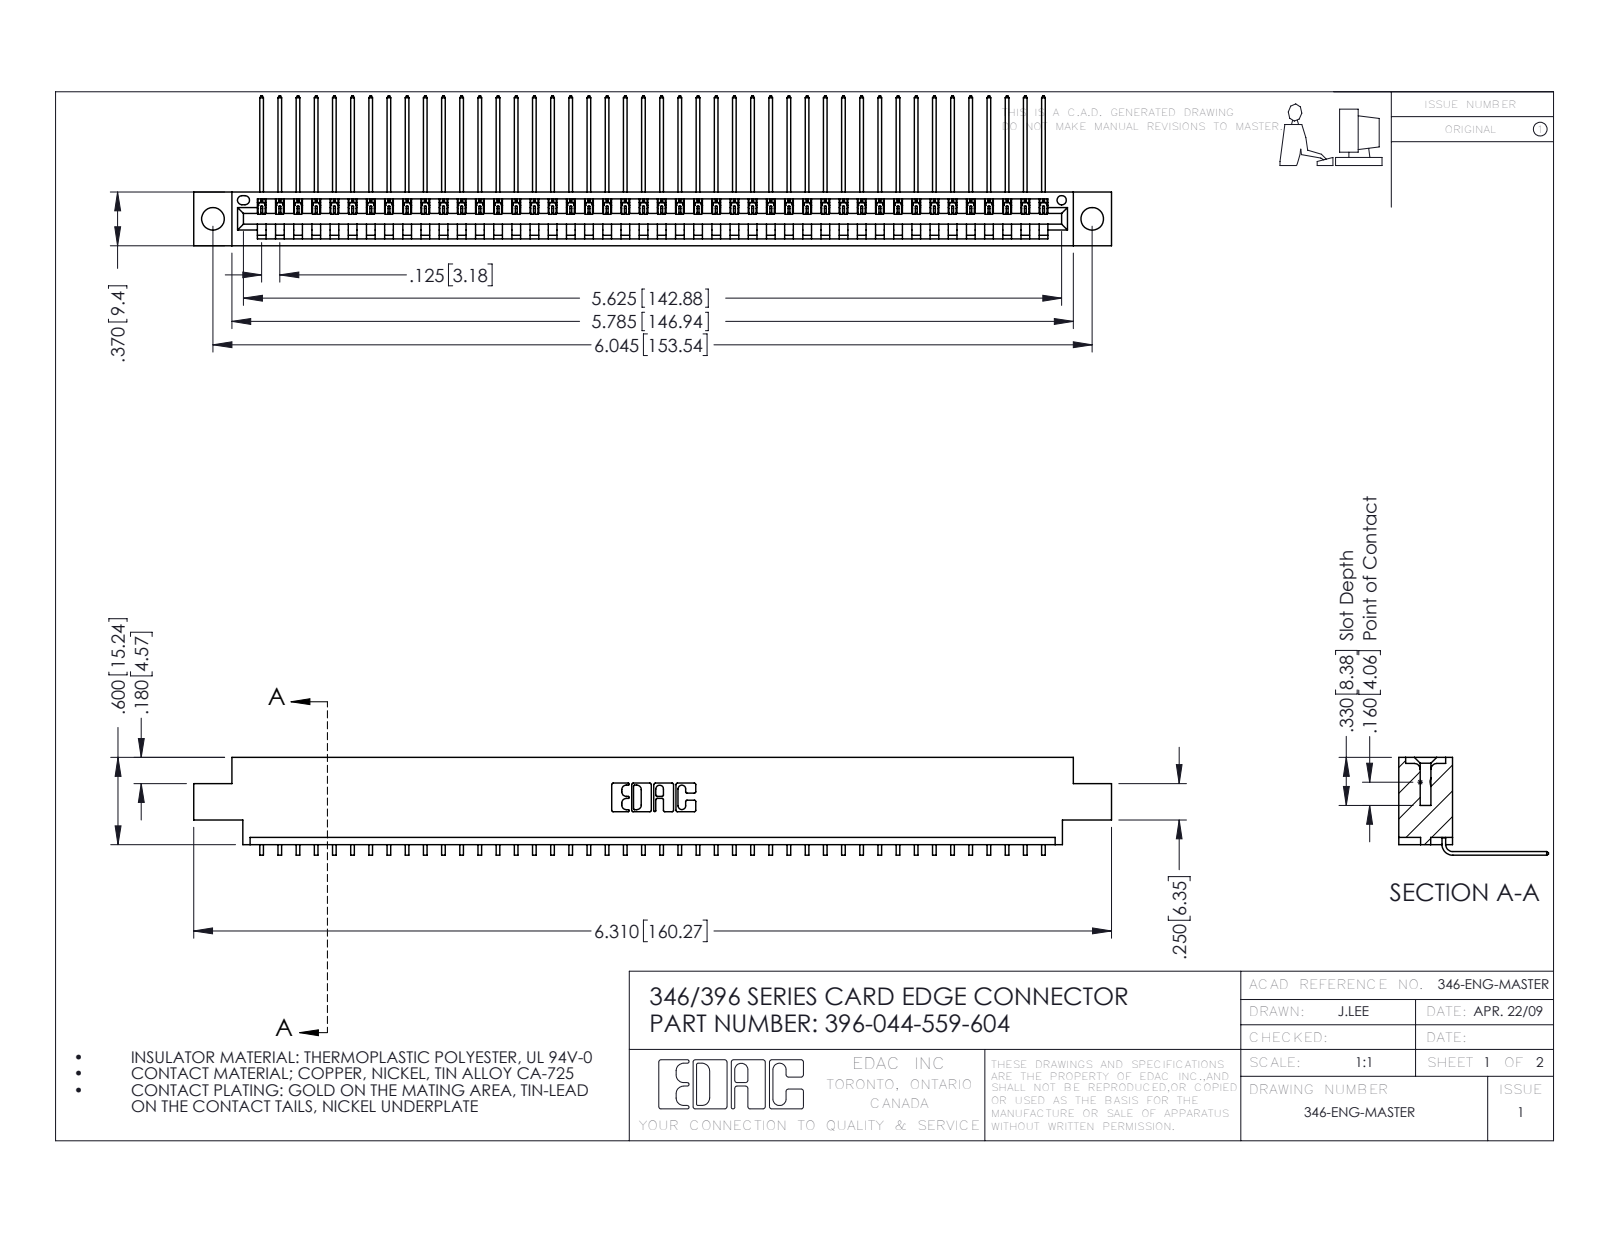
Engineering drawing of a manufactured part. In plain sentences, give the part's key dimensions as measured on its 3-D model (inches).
The part is named "345-292-001_558 559 Tail - 1; 346 Part_0.170 Offset - 0.156 Dia-TH; 396-044-559-604". Its 3-D file was written by "SolidWorks 2016 (CONFIG_CONTROL_DESIGN)". It is 45 solids with 2766 faces: 1928 planar, 838 cylindrical and 0 other. Overall it measures 6.31 by 1.03 by 0.673 inches. Its volume is 0.931 cubic inches and its surface area 30.9 square inches. Round holes: 2 of diameter 0.156, 1 of diameter 0.064. Partial cylindrical surfaces (rounded edges, fillets, slot ends): 88 of radius 0.006, 22 of radius 0.01, 6 of radius 0.007, 6 of radius 0.031, 3 of radius 0.026, 2 of radius 0.031, 2 of radius 0.04, 1 of radius 0.014. The main face-to-face distances are 0.048, 0.322, 0.37, 0.025, 0.25, 0.072, 0.298, 0.148, 0.222, 0.1. The hole center spacings are 0.246, 5.836, 6.045.
